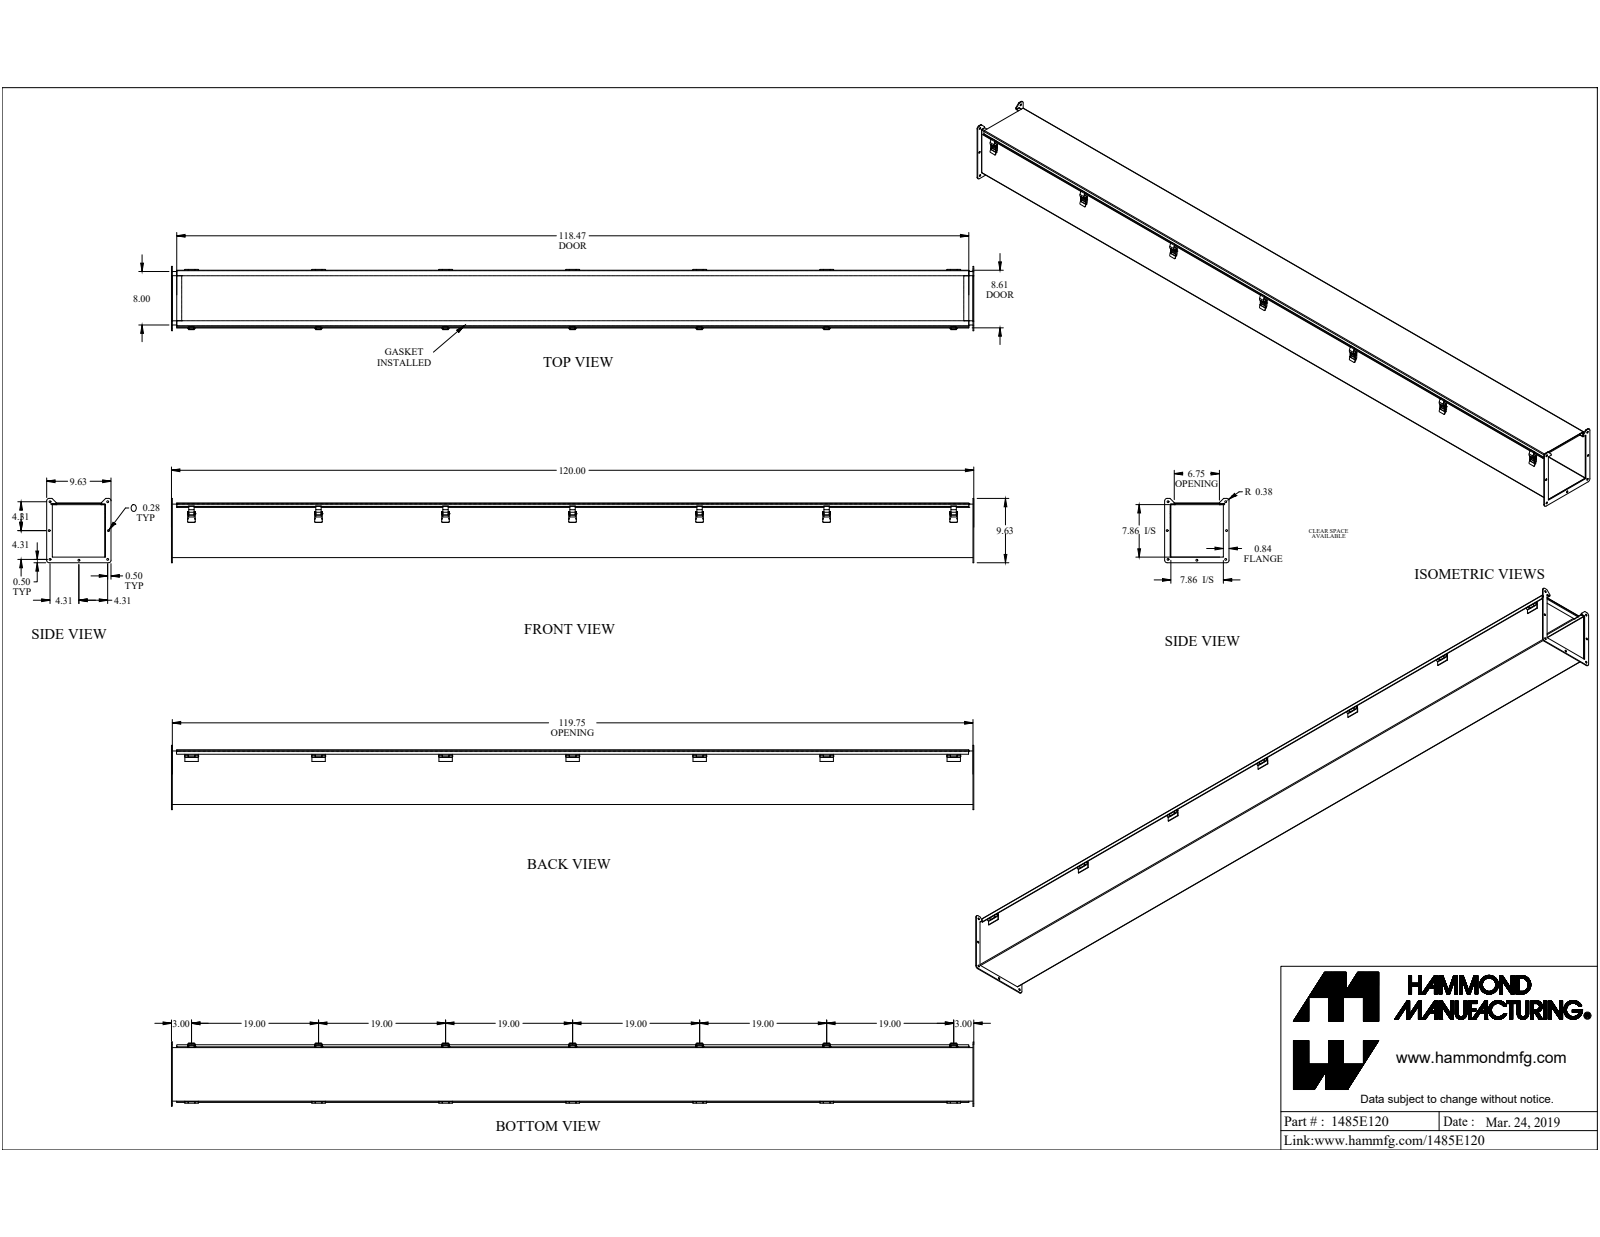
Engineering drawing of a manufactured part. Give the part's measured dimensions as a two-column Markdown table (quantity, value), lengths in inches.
| quantity | value |
| --- | --- |
| part name | 1485E120 |
| STEP written by | SolidWorks 2019 (CONFIG_CONTROL_DESIGN) |
| units | inches |
| bodies | 50 solids, 1141 faces (670 planar, 457 cylindrical, 14 other) |
| overall size | 120 × 9.625 × 9.625 |
| volume | 341.6 in³ |
| surface area | 9 001 in² |
| round holes (diameter × count) | 0.281 × 7, 0.125 × 1, 0.13 × 1, 0.164 × 1 |
| round bosses / shafts (diameter × count) | 0.187 × 2, 0.275 × 1, 0.156 × 1, 0.125 × 1, 0.125 × 1 |
| partial cylindrical surfaces (radius × count) | 0.016 × 43, 0.125 × 19, 0.035 × 15, 0.039 × 15, 0.076 × 15, 0.015 × 14, 0.029 × 14, 0.086 × 14 |
| main face-to-face distances | 0.072, 7.928, 8.1, 8, 7.856, 8.028, 8.172, 0.172, 7.913, 7.841 |
| hole center spacings | 8.625, 4.314, 4.315, 9.755, 9.755, 6.276, 12.197, 0.285 |
